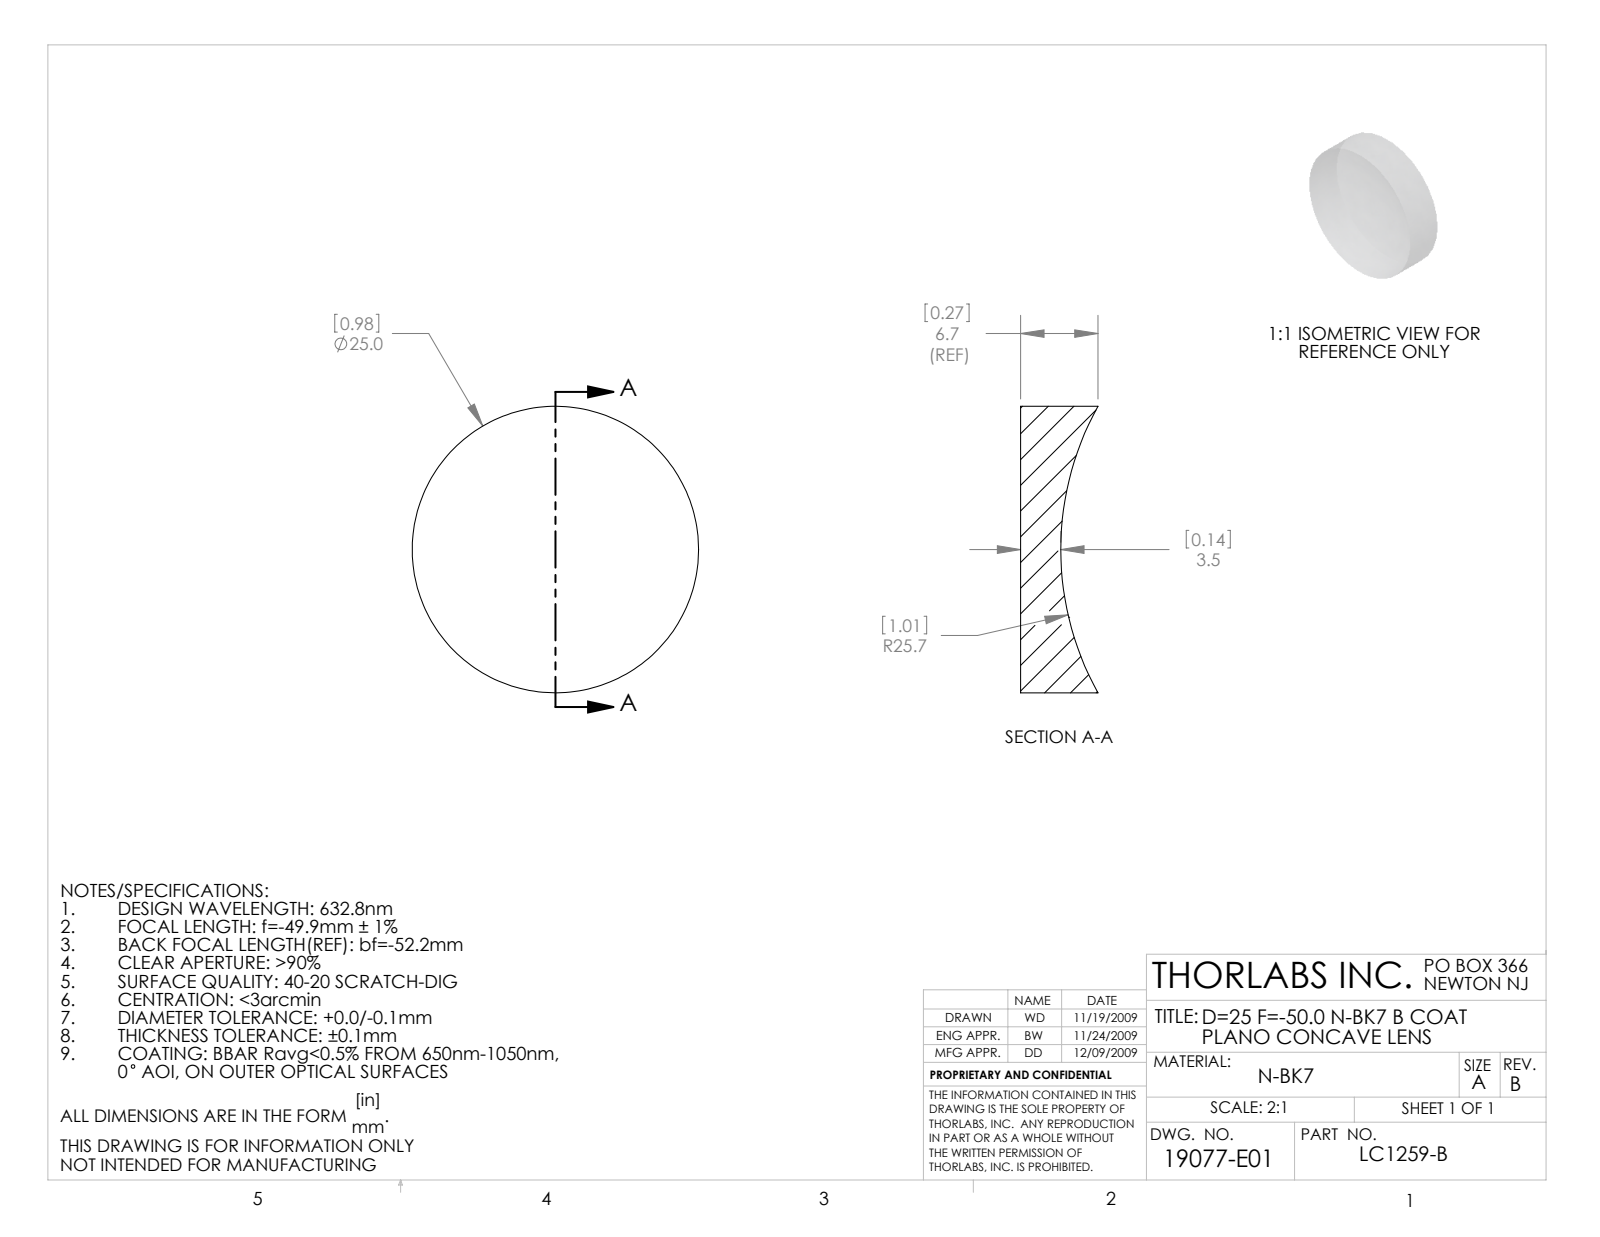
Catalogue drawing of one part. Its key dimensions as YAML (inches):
part_name: "19077-E0W"
step_written_by: "SolidWorks 2009 (AUTOMOTIVE_DESIGN)"
units: inches
bodies: {solids: 1, faces: 5, planar: 1, cylindrical: 2, other: 2}
overall_size: [0.984, 0.984, 0.266]
volume: 0.152
surface_area: 2.395
round_bosses_or_shafts:
  - {diameter: 0.984, count: 1}
